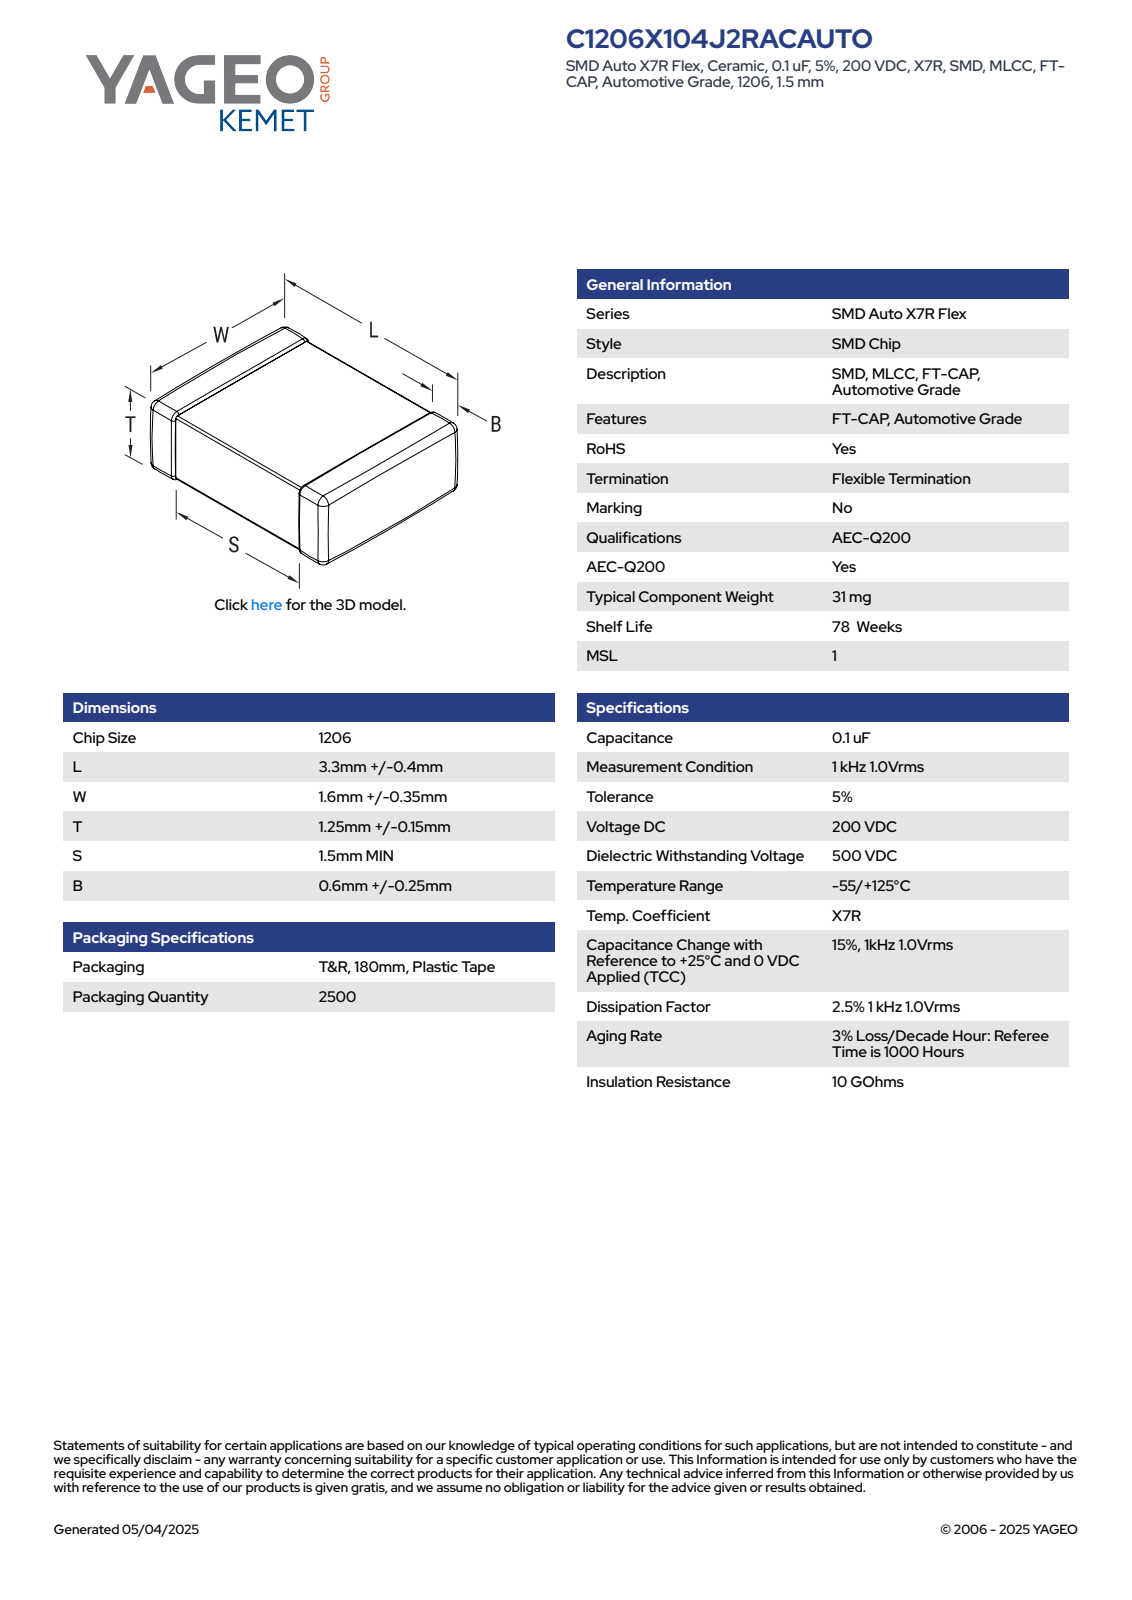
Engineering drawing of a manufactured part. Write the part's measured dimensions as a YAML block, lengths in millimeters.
part_name: "CCS_CCSTDNOS_1206_L3.7W1.95T1.4B0.85"
step_written_by: "SolidWorks 2014 (AUTOMOTIVE_DESIGN)"
units: millimeters
bodies: {solids: 4, faces: 125, planar: 71, cylindrical: 38, other: 16}
overall_size: [3.7, 1.95, 1.4]
volume: 10
surface_area: 30
face_to_face_distances: [1.36, 1.91, 1.32, 1.4, 1.87, 3.7, 1.95, 0.86, 0.82, 1.05]
